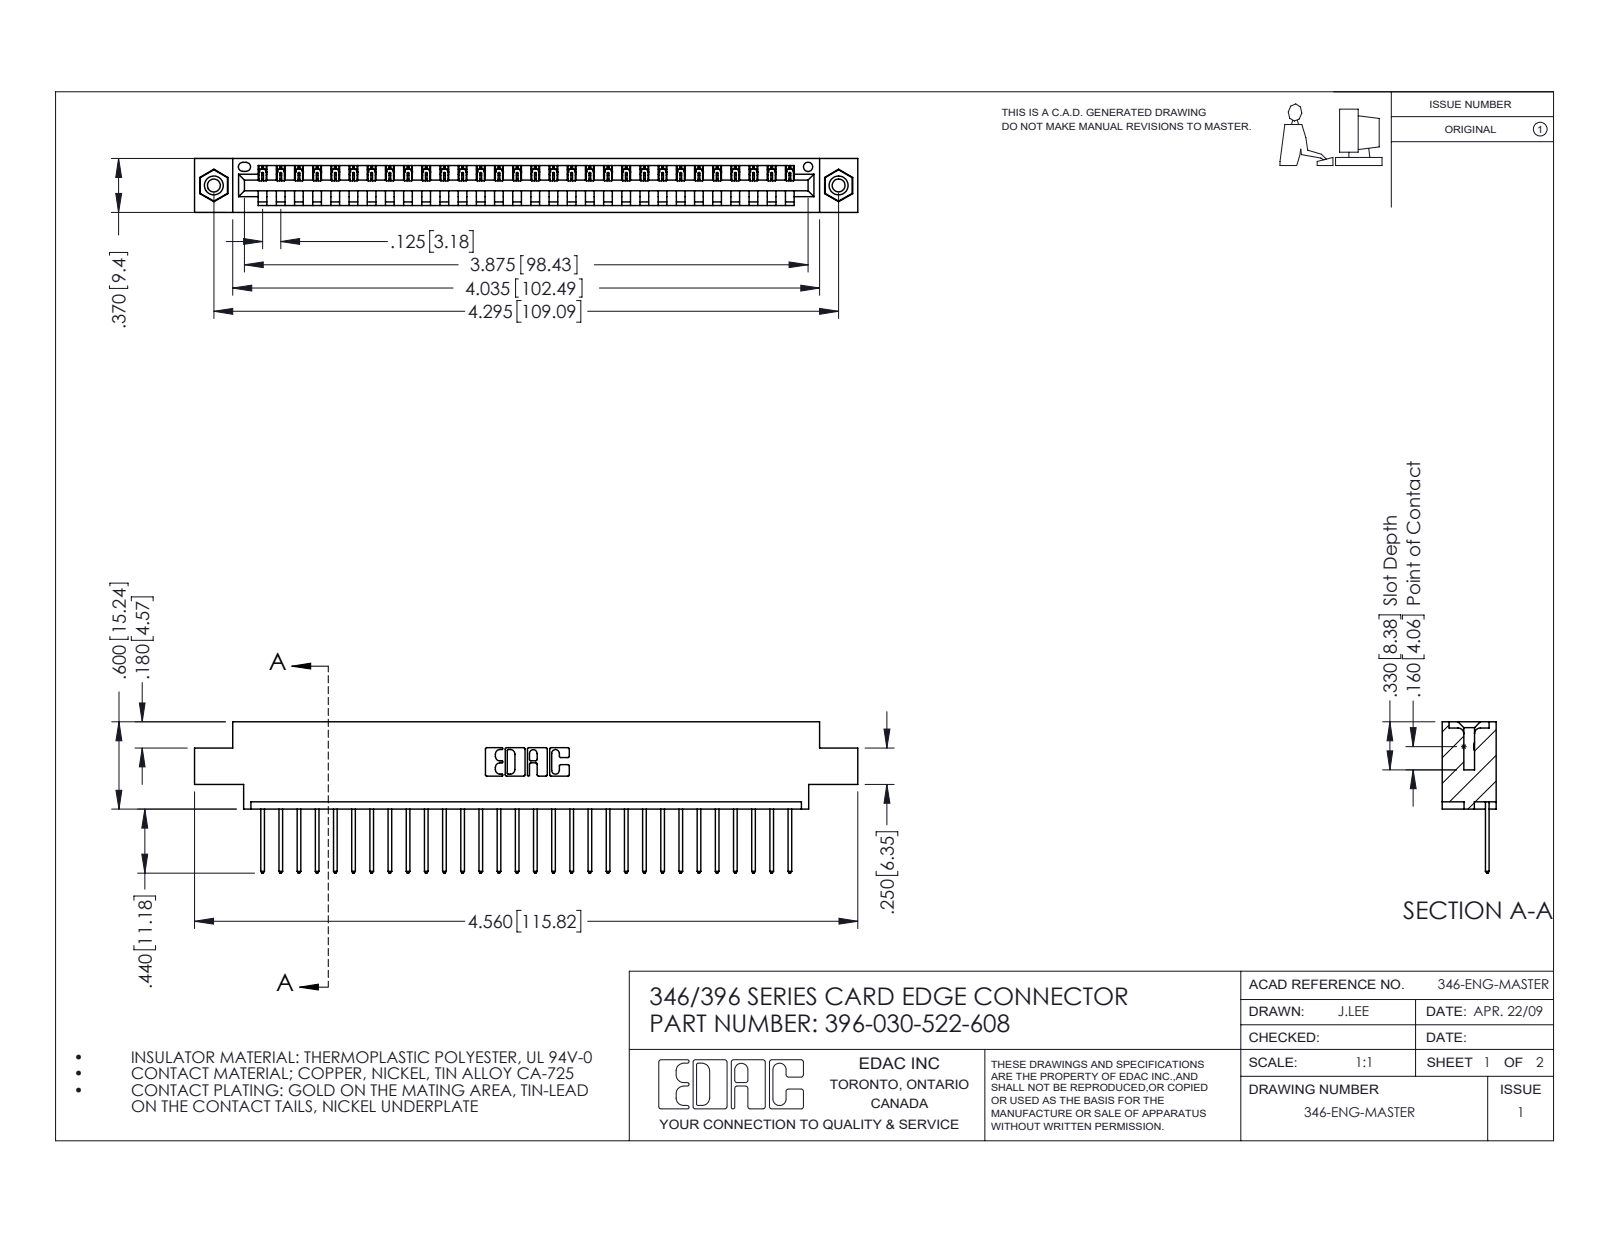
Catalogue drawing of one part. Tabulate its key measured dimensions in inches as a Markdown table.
| quantity | value |
| --- | --- |
| part name | 346 Part_0.170 Offset - 0.156 Dia-TI; 345-250-001_345-250-003-102; 345-292-001_345-293-122; 396-030-522-608 |
| STEP written by | SolidWorks 2016 (CONFIG_CONTROL_DESIGN) |
| units | inches |
| bodies | 33 solids, 1926 faces (1312 planar, 598 cylindrical, 16 other) |
| overall size | 4.56 × 1.04 × 0.37 |
| volume | 0.662 in³ |
| surface area | 21.27 in² |
| round holes (diameter × count) | 0.089 × 2, 0.125 × 2, 0.156 × 2, 0.064 × 1 |
| round bosses / shafts (diameter × count) | 0.155 × 2 |
| partial cylindrical surfaces (radius × count) | 0.006 × 60, 0.01 × 60, 0.01 × 22, 0.007 × 6, 0.031 × 6, 0.026 × 3, 0.031 × 2, 0.04 × 2 |
| main face-to-face distances | 0.048, 0.322, 0.37, 0.25, 0.072, 0.298, 0.025, 0.222, 0.148, 0.1 |
| hole center spacings | 0.246, 4.087, 4.295 |
